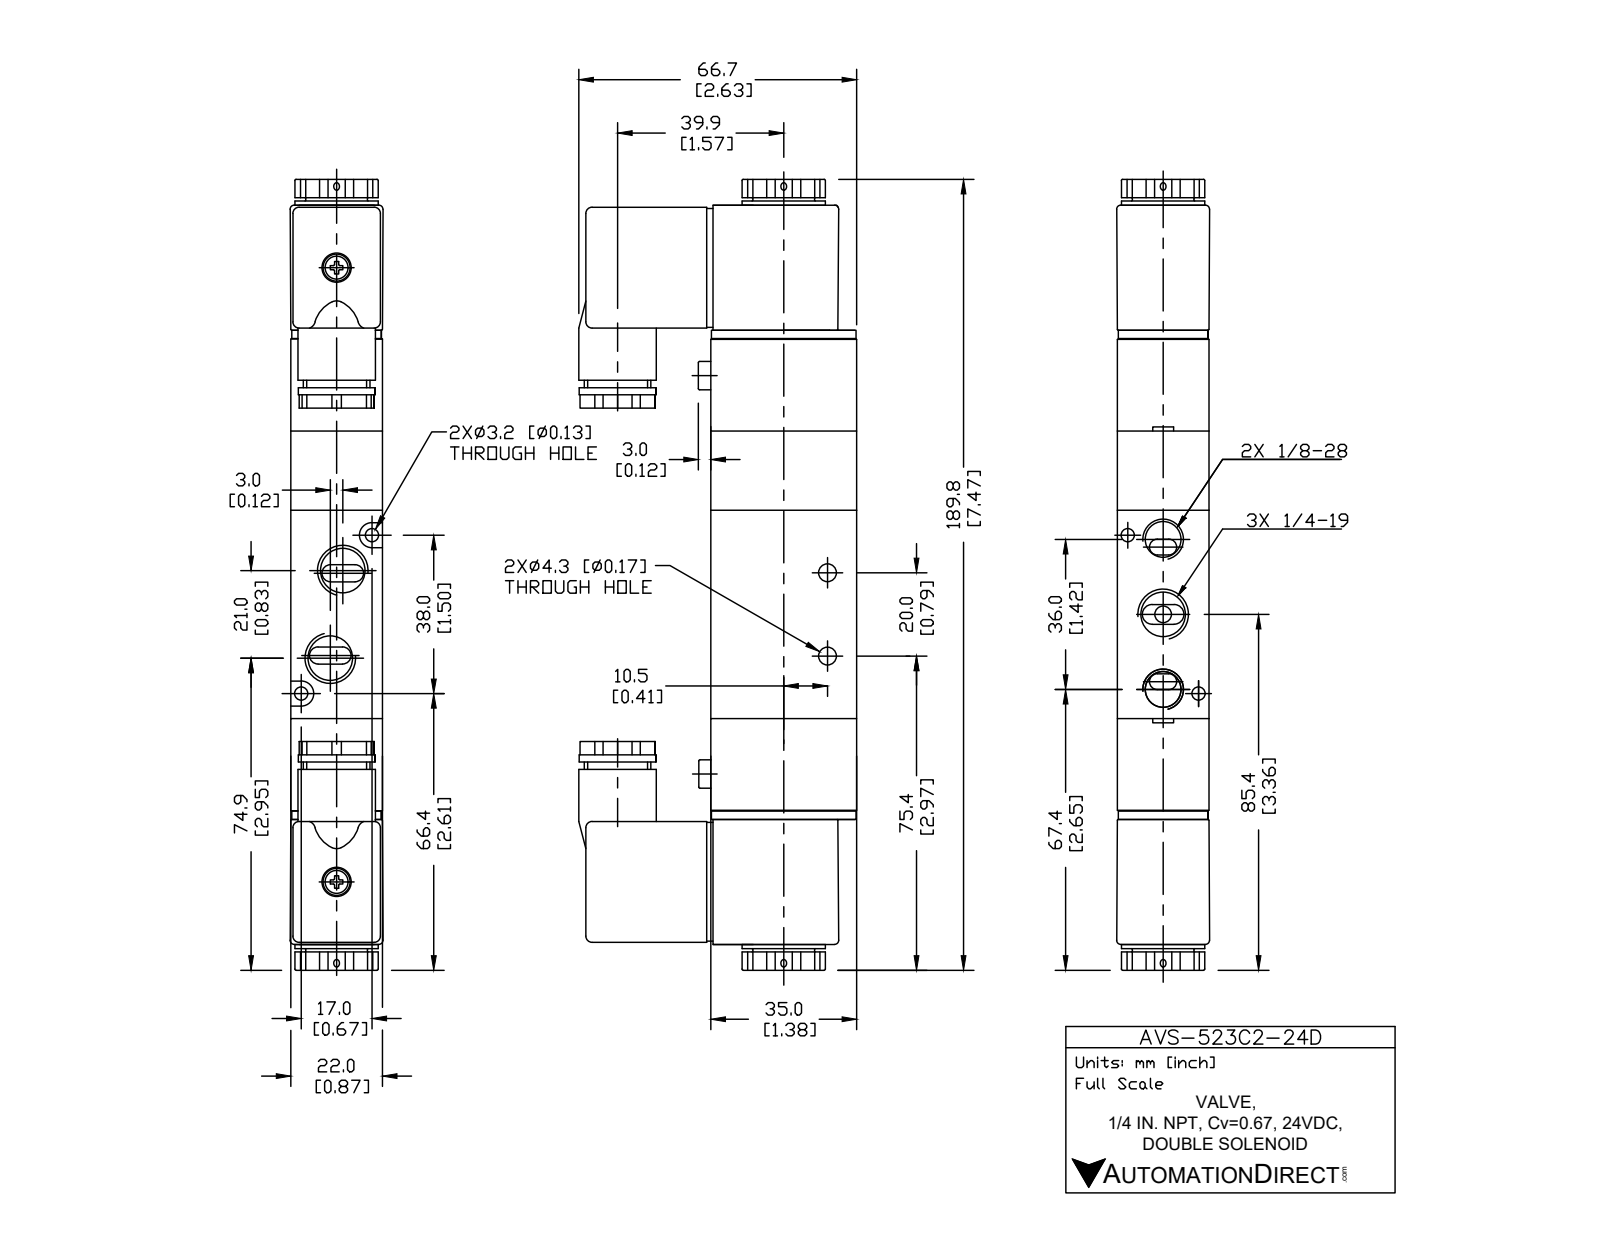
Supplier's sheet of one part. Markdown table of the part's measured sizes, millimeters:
| quantity | value |
| --- | --- |
| part name | AVS-523C2-24D |
| STEP written by | SolidWorks 2015 (CONFIG_CONTROL_DESIGN) |
| units | millimeters |
| bodies | 5 solids, 236 faces (129 planar, 91 cylindrical, 16 other) |
| overall size | 189.82 × 66.7 × 22 |
| volume | 148 738 mm³ |
| surface area | 37 934 mm² |
| round holes (diameter × count) | 11.13 × 3, 3.2 × 2, 4.3 × 2, 8.43 × 2, 9.3 × 1 |
| round bosses / shafts (diameter × count) | 6.8 × 2, 18.6 × 1, 17.6 × 1, 15.81 × 1, 13.02 × 1, 11 × 1 |
| partial cylindrical surfaces (radius × count) | 1.54 × 10, 0.3 × 8, 0.5 × 8, 1 × 8, 3 × 2 |
| main face-to-face distances | 0.88, 21.74, 1.95, 20.05, 22, 18.1, 22.62, 69, 30.59, 5.03 |
| hole center spacings | 8.56, 18, 20.81, 37.96, 7.54, 7.83, 10.53, 10.55 |
